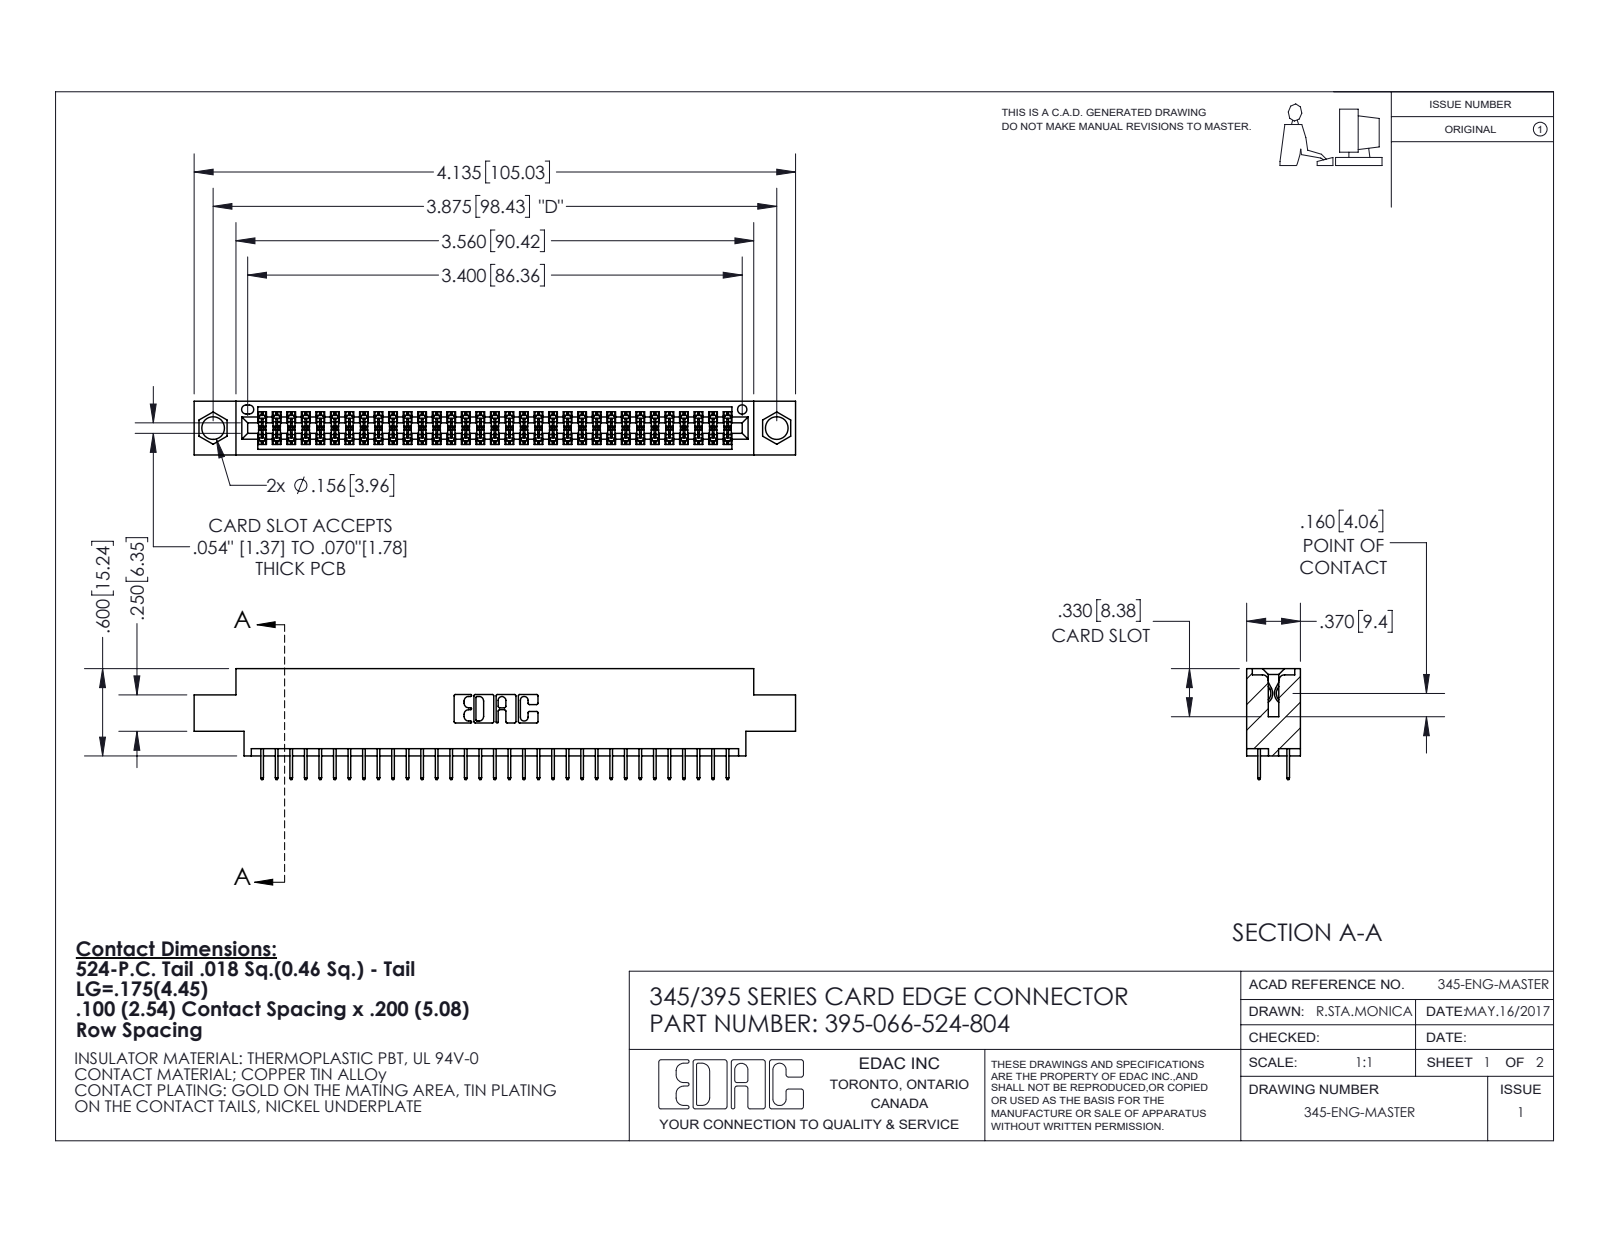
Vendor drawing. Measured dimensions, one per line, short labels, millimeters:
name: 345-292-001_345-293-124; 395-066-524-804; 345 Part_0.170 Offset - 0.156 Dia-TI
written by: SolidWorks 2020 (CONFIG_CONTROL_DESIGN)
unit: mm
bodies: 67 solids, 3708 faces (2672 planar, 1036 cylindrical, 0 other)
size: 105 × 19.4 × 9.4
volume: 9 800 mm³; area: 14 050 mm²
holes: 2× ⌀4, 1× ⌀1.6
rounds: 99× R0.2, 22× R0.3, 6× R0.2, 6× R0.8, 3× R0.7, 2× R0.4, 2× R0.5, 2× R0.6
face distances: 1.8, 7.6, 9.4, 5.1, 2.5, 6.9, 0.6, 5.7, 4.4, 1.8
hole spacings: 6.9, 92.5, 98.4
